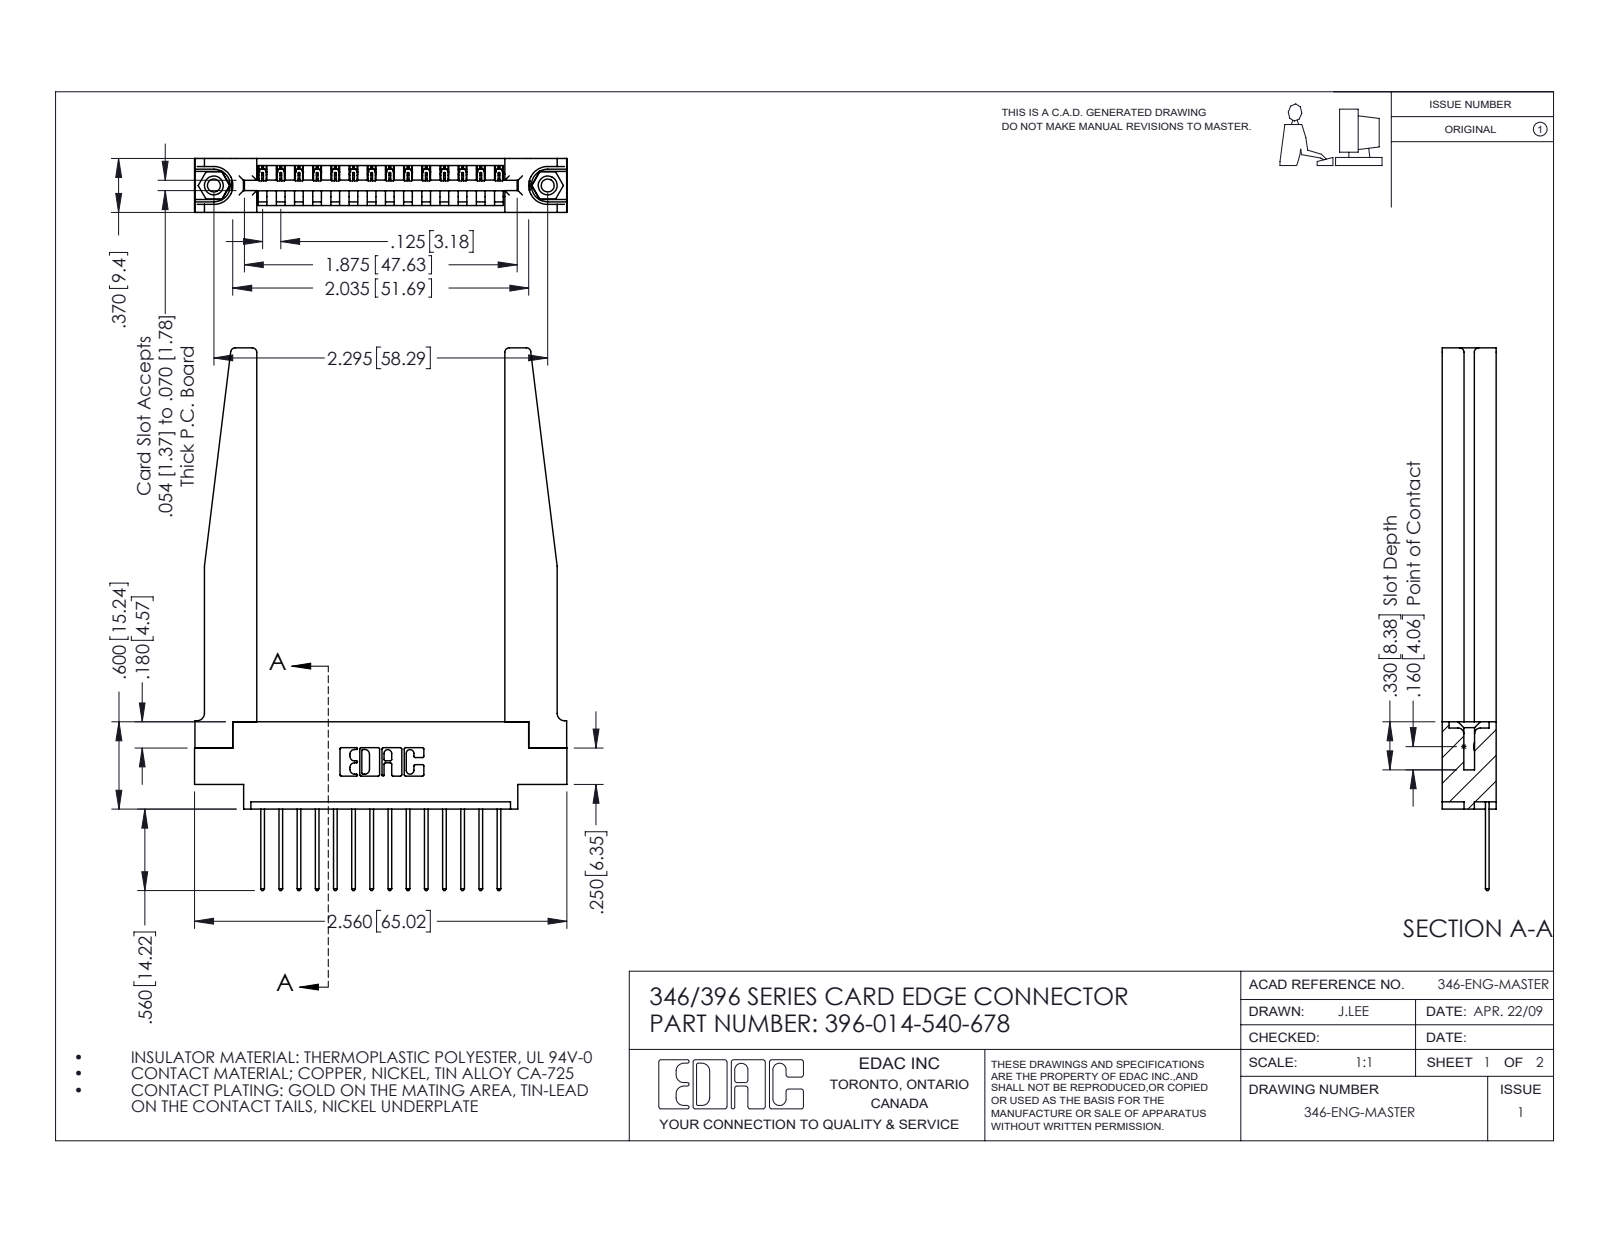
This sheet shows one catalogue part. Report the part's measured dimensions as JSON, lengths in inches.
{"part_name": "346 Part_0.170 Offset - 0.156 Dia-TH; 396-014-540-678; 346-220-078_345-220-078; 345-292-001_345-293-140 (+1 more)", "step_written_by": "SolidWorks 2016 (CONFIG_CONTROL_DESIGN)", "units": "inches", "bodies": {"solids": 19, "faces": 1172, "planar": 782, "cylindrical": 338, "other": 52}, "overall_size": [3.73, 2.56, 0.37], "volume_in3": 0.781, "surface_area_in2": 21.55, "round_holes": [[0.089, 2], [0.125, 2], [0.156, 2], [0.064, 1]], "round_bosses_or_shafts": [[0.155, 2]], "partial_cylinders_radius": [[0.006, 28], [0.01, 28], [0.01, 22], [0.03, 8], [0.007, 6], [0.031, 6], [0.026, 3], [0.031, 2]], "face_to_face_distances": [0.37, 0.15, 0.072, 0.048, 0.322, 0.148, 0.25, 0.102, 0.22, 0.173], "hole_center_spacings": [0.246, 2.089, 2.295]}
